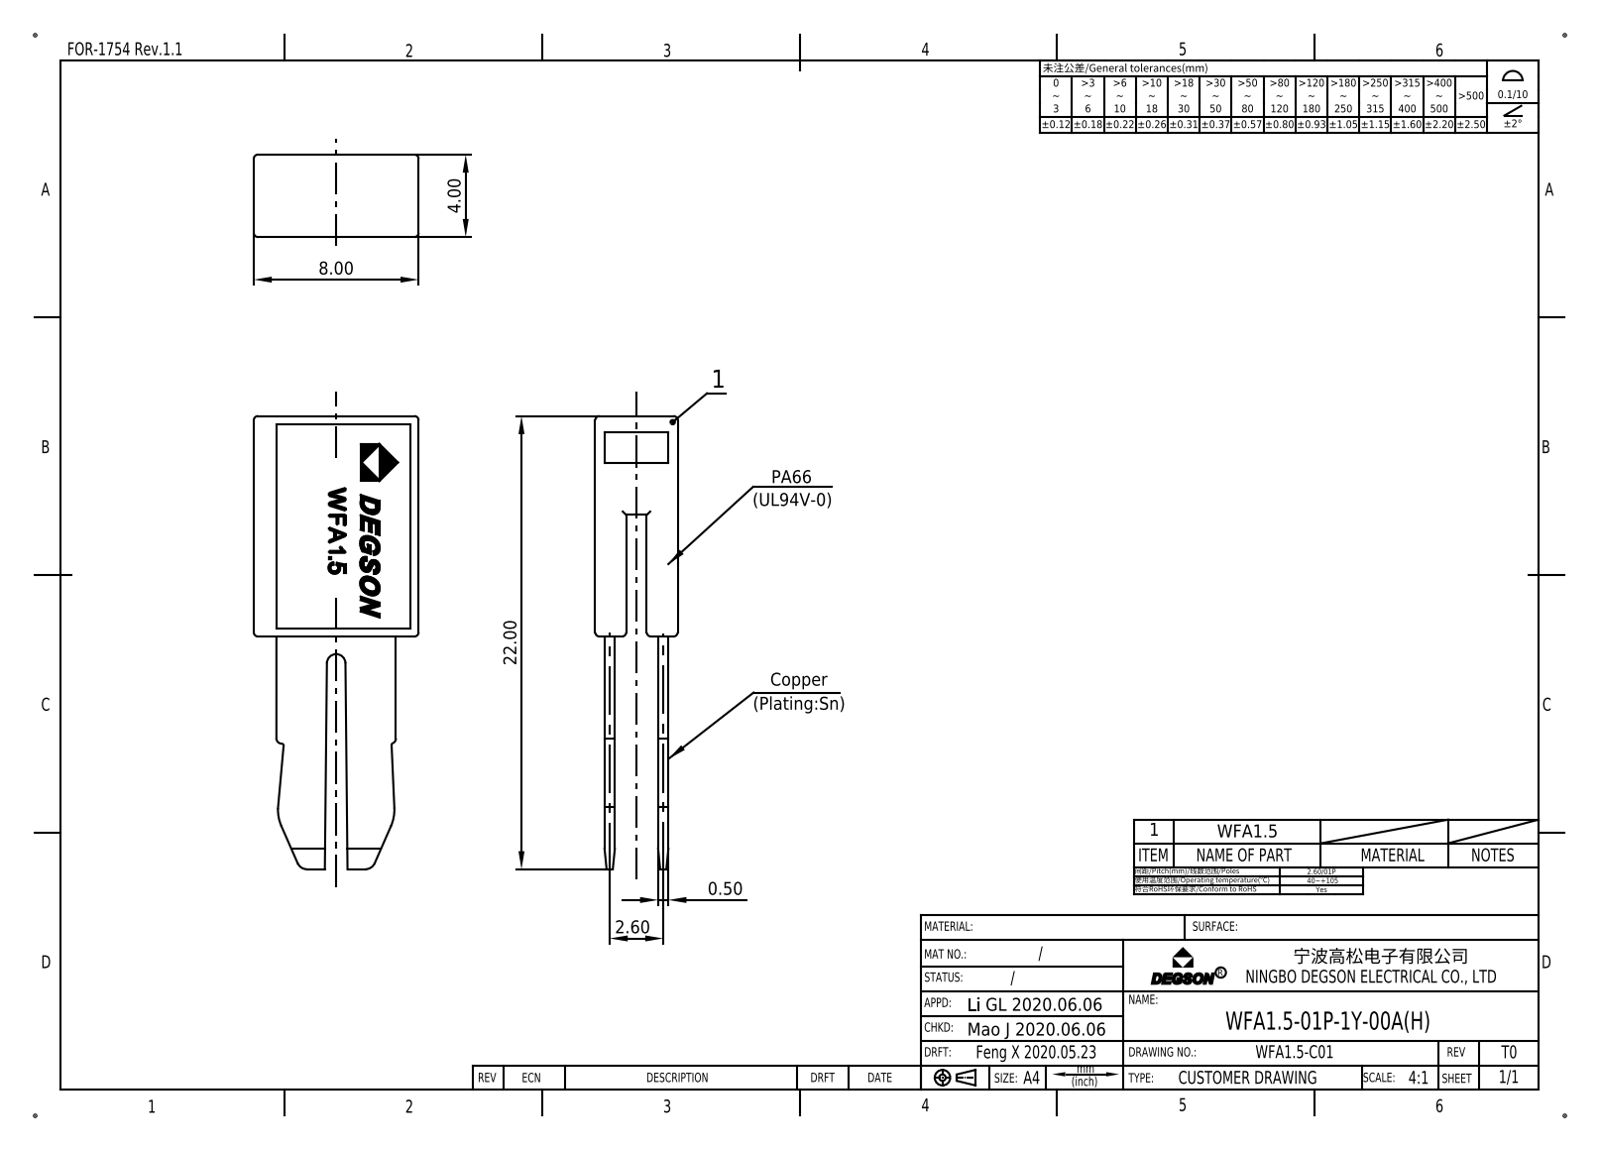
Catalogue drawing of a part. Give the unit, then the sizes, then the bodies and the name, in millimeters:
Units: millimetres
Overall size (bounding box): 22 × 8 × 4
Partial cylindrical surfaces — rounded edges, fillets, slot ends (radius × count): R0.2 ×20, R0.1 ×2, R0.25 ×2, R0.5 ×2, R2 ×2
Main face-to-face distances: 0.45, 3.55, 0.95, 3.05, 0.5, 2.6, 1.5, 2.5, 1.05, 2.05
Volume: 327 mm³ · Surface area: 713 mm²
Bodies: 1 solid, 92 faces (38 planar, 42 cylindrical, 12 other)
Part name (STEP PRODUCT): WFA1_5-01P-1Y-00A_H
STEP written by: PRO/ENGINEER BY PARAMETRIC TECHNOLOGY CORPORATION, 2014000 (CONFIG_CONTROL_DESIGN)
